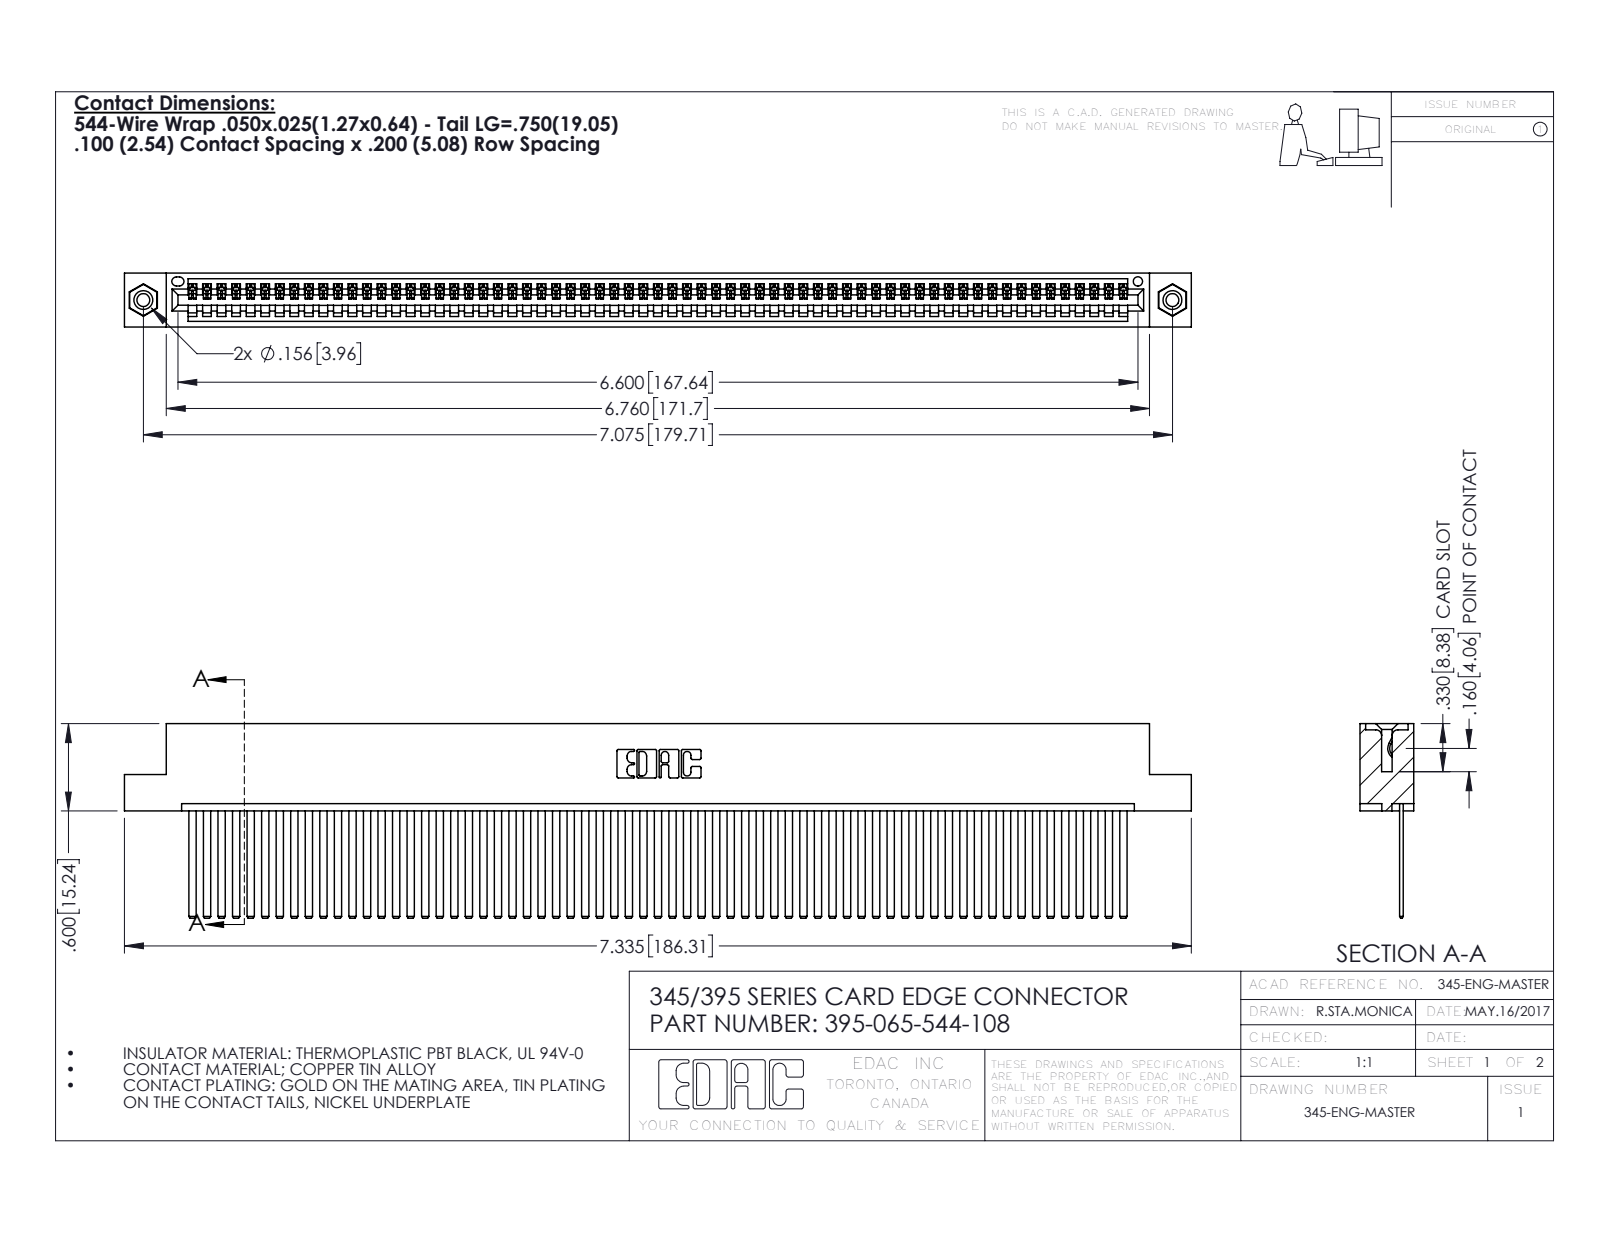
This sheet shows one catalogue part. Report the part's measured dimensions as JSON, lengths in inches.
{"part_name": "345-250-001_345-250-003-102; 345-292-001_345-293-144; 395-065-544-108; 345 Part_Flush Mounting Lugs - 0.156 Dia-TI", "step_written_by": "SolidWorks 2016 (CONFIG_CONTROL_DESIGN)", "units": "inches", "bodies": {"solids": 68, "faces": 3566, "planar": 2452, "cylindrical": 1098, "other": 16}, "overall_size": [7.335, 1.337, 0.37], "volume_in3": 1.137, "surface_area_in2": 42.39, "round_holes": [[0.089, 2], [0.125, 2], [0.156, 2], [0.064, 1]], "round_bosses_or_shafts": [[0.155, 2]], "partial_cylinders_radius": [[0.006, 130], [0.01, 22], [0.007, 6], [0.031, 6], [0.026, 3], [0.031, 2], [0.04, 2], [0.014, 1]], "face_to_face_distances": [0.072, 0.298, 0.025, 0.098, 0.272, 0.37, 0.2, 0.225, 0.149, 0.072], "hole_center_spacings": [0.27, 6.839, 7.075]}
